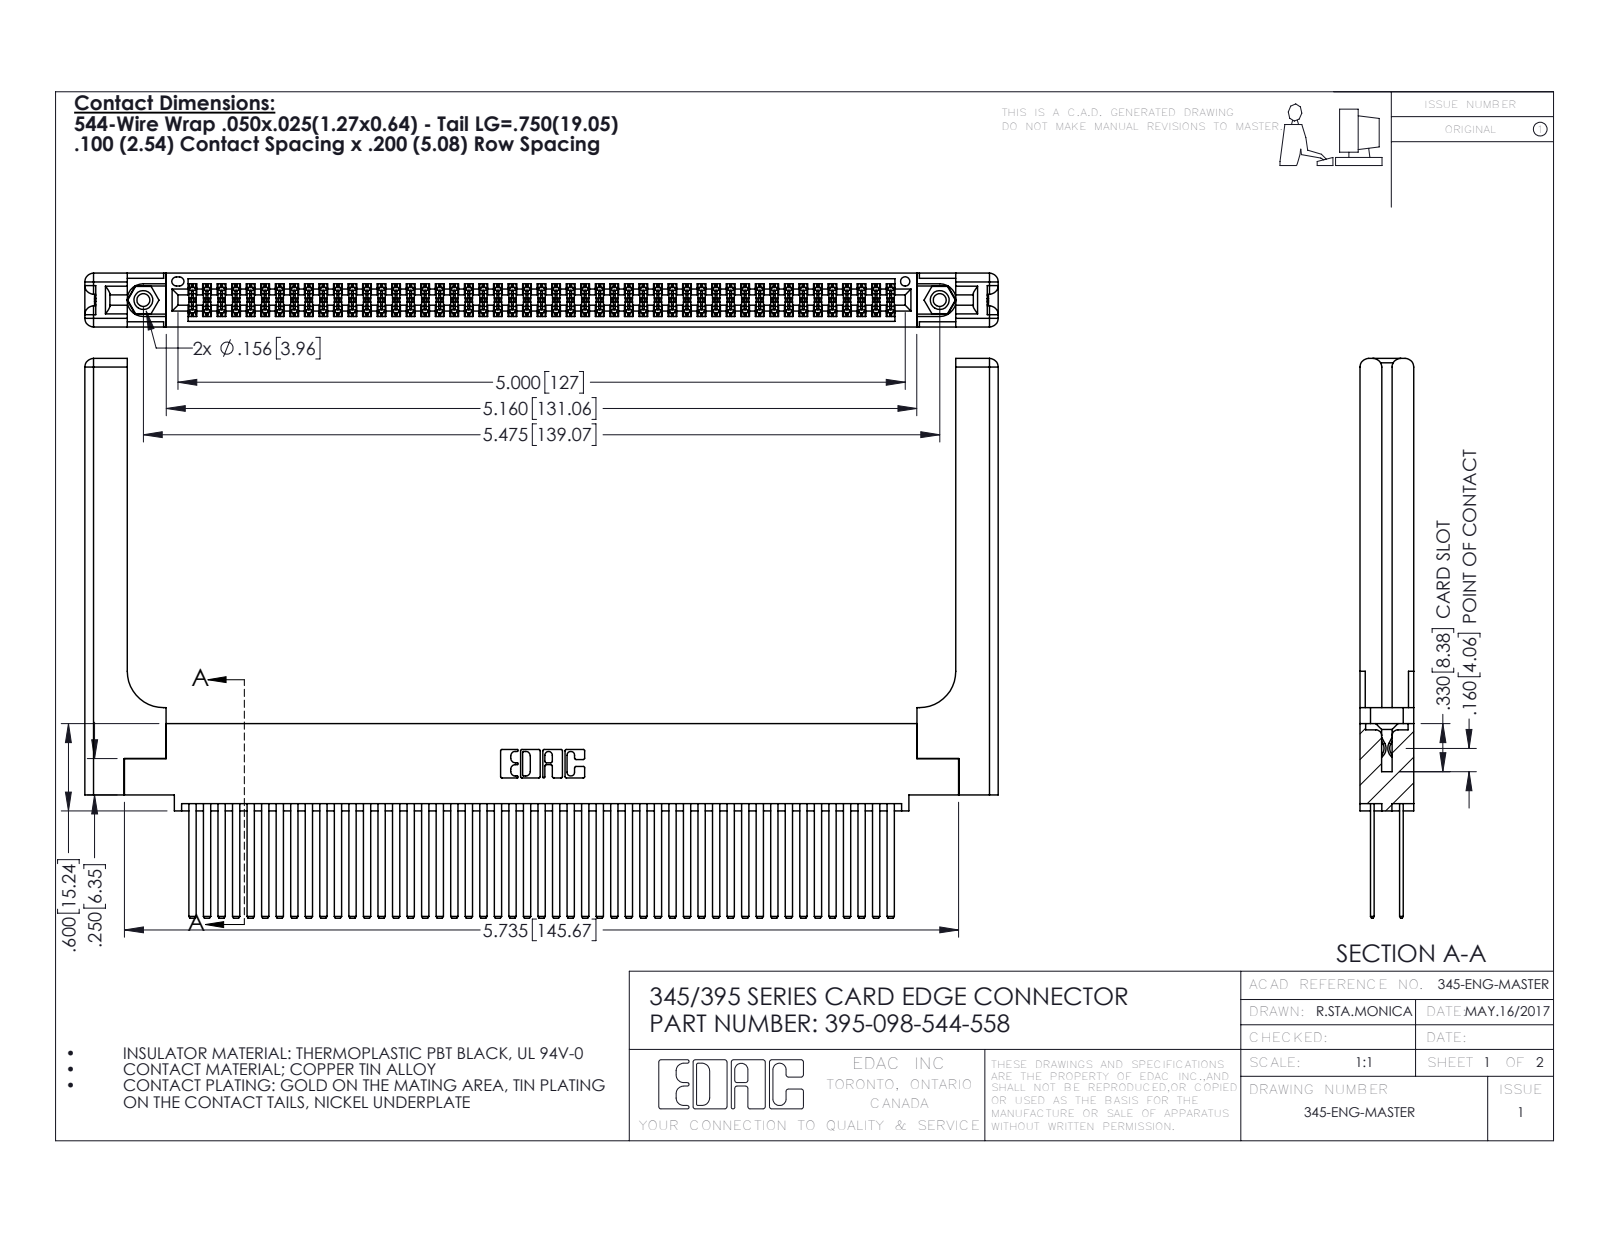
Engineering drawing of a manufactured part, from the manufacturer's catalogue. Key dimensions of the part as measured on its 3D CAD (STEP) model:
Part name (STEP PRODUCT): 395-098-544-558; 345-250-001_345-250-001-102; 345 Part_0.110 Offset - 0.156 Dia-TH; 345-292-001_345-293-144 (+1 more)
STEP written by: SolidWorks 2016 (CONFIG_CONTROL_DESIGN)
Units: inches
Bodies: 103 solids, 4698 faces (3074 planar, 1564 cylindrical, 60 other)
Overall size (bounding box): 6.279 × 3.847 × 0.37
Volume: 1.546 in³ · Surface area: 53.06 in²
Round holes (diameter × count): ⌀0.089 ×2, ⌀0.125 ×2, ⌀0.156 ×2, ⌀0.064 ×1
Round bosses / shafts (diameter × count): ⌀0.155 ×2
Partial cylindrical surfaces — rounded edges, fillets, slot ends (radius × count): R0.006 ×147, R0.01 ×22, R0.06 ×16, R0.007 ×6, R0.031 ×6, R0.026 ×3, R0.014 ×2, R0.019 ×2
Main face-to-face distances: 0.072, 0.298, 0.098, 0.272, 0.025, 0.2, 0.37, 0.225, 0.175, 0.148
Hole centre spacings: 0.27, 5.239, 5.475
